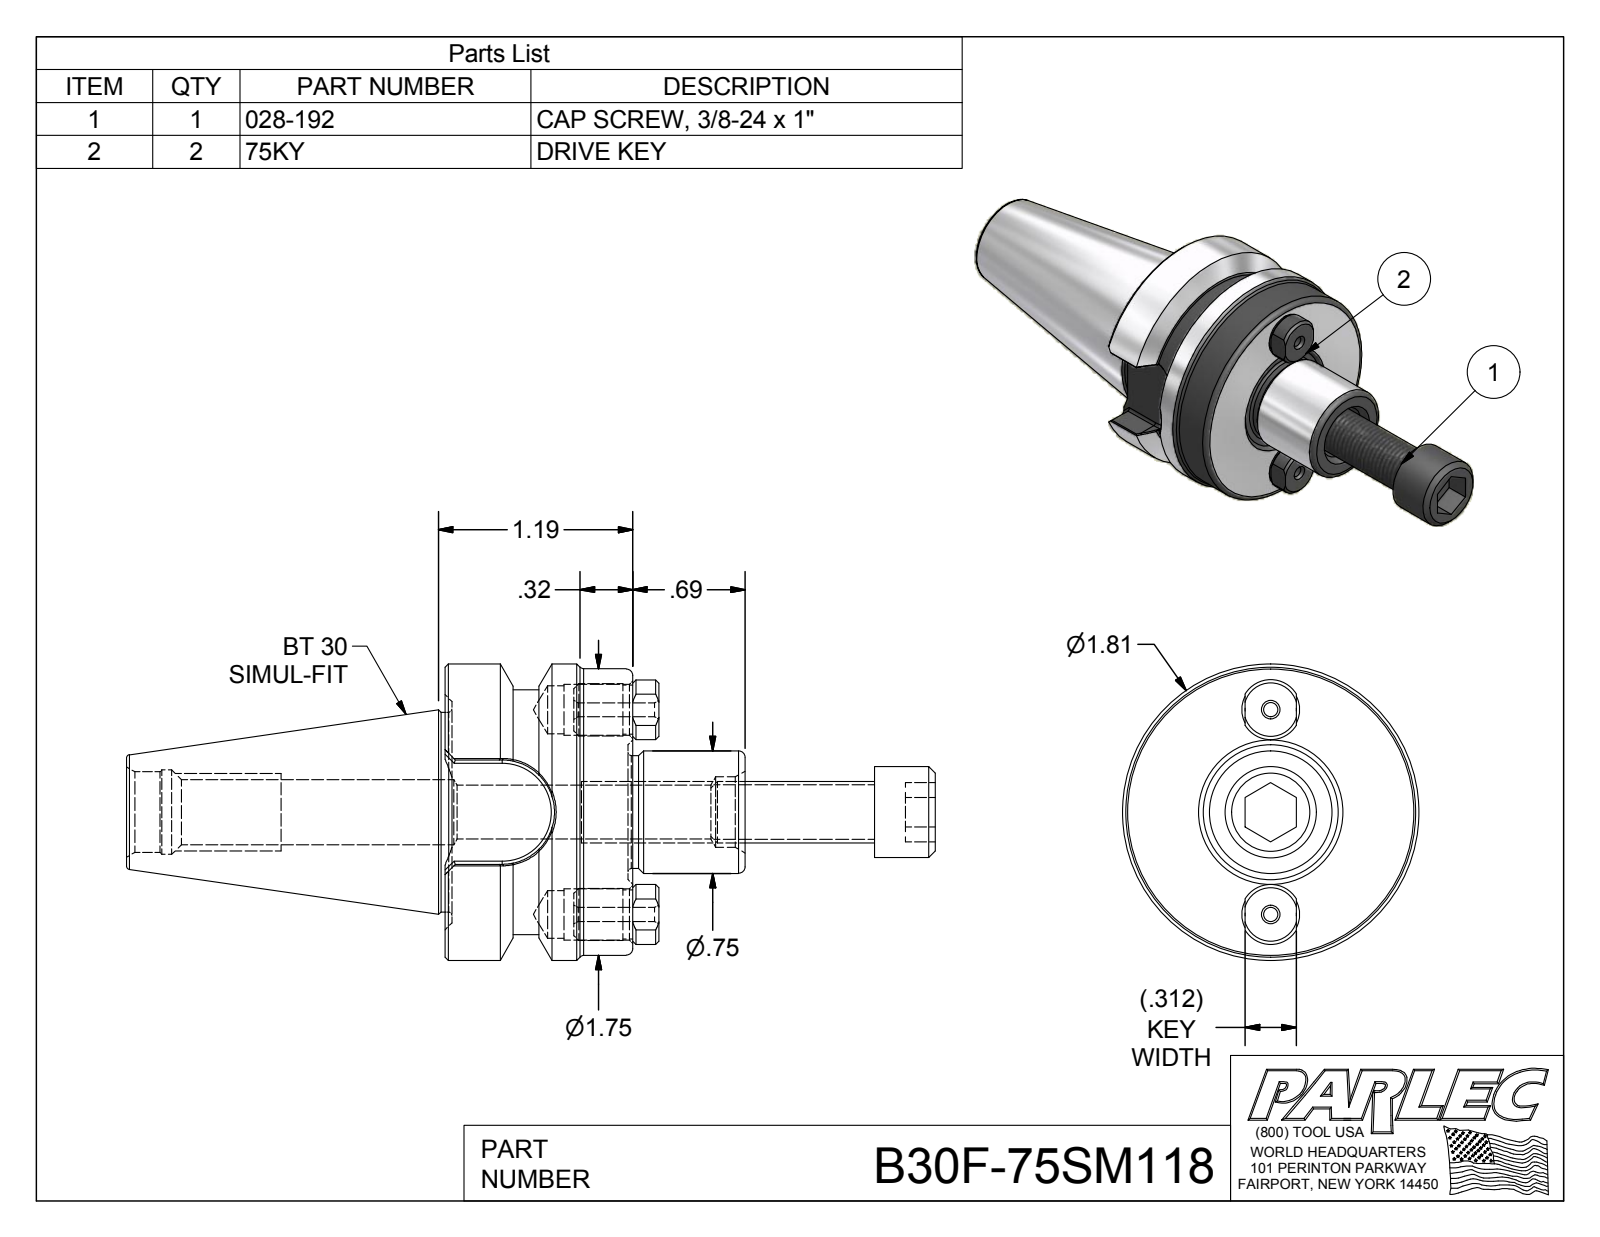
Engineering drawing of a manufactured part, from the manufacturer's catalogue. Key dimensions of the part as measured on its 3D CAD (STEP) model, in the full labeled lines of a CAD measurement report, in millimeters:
Part name (STEP PRODUCT): B30F-75SM118; B30F-75SM118-1; 75KY; 028-192
STEP written by: Autodesk Inventor 2012 (AUTOMOTIVE_DESIGN)
Units: millimetres
Bodies: 4 solids, 154 faces (49 planar, 40 cylindrical, 65 other)
Overall size (bounding box): 125.5 × 46 × 46
Volume: 66 910 mm³ · Surface area: 18 450 mm²
Round holes (diameter × count): ⌀2.1 ×2, ⌀7.4 ×2, ⌀7.9 ×2, ⌀8.4 ×1, ⌀10.1 ×1, ⌀10.9 ×1, ⌀12.5 ×1, ⌀13.1 ×1
Round bosses / shafts (diameter × count): ⌀8.1 ×2, ⌀7.6 ×2, ⌀46 ×1, ⌀44.5 ×1, ⌀31 ×1, ⌀19.1 ×1, ⌀17.5 ×1, ⌀14.1 ×1
Partial cylindrical surfaces — rounded edges, fillets, slot ends (radius × count): R0.5 ×8, R4.6 ×2, R8.1 ×1, R19 ×1
Main face-to-face distances: 29.2, 32.6, 4.8, 38.3, 1.1, 28.1, 46.6, 45.5, 17.4, 33.2
Hole centre spacings: 15.9, 15.9, 31.8
